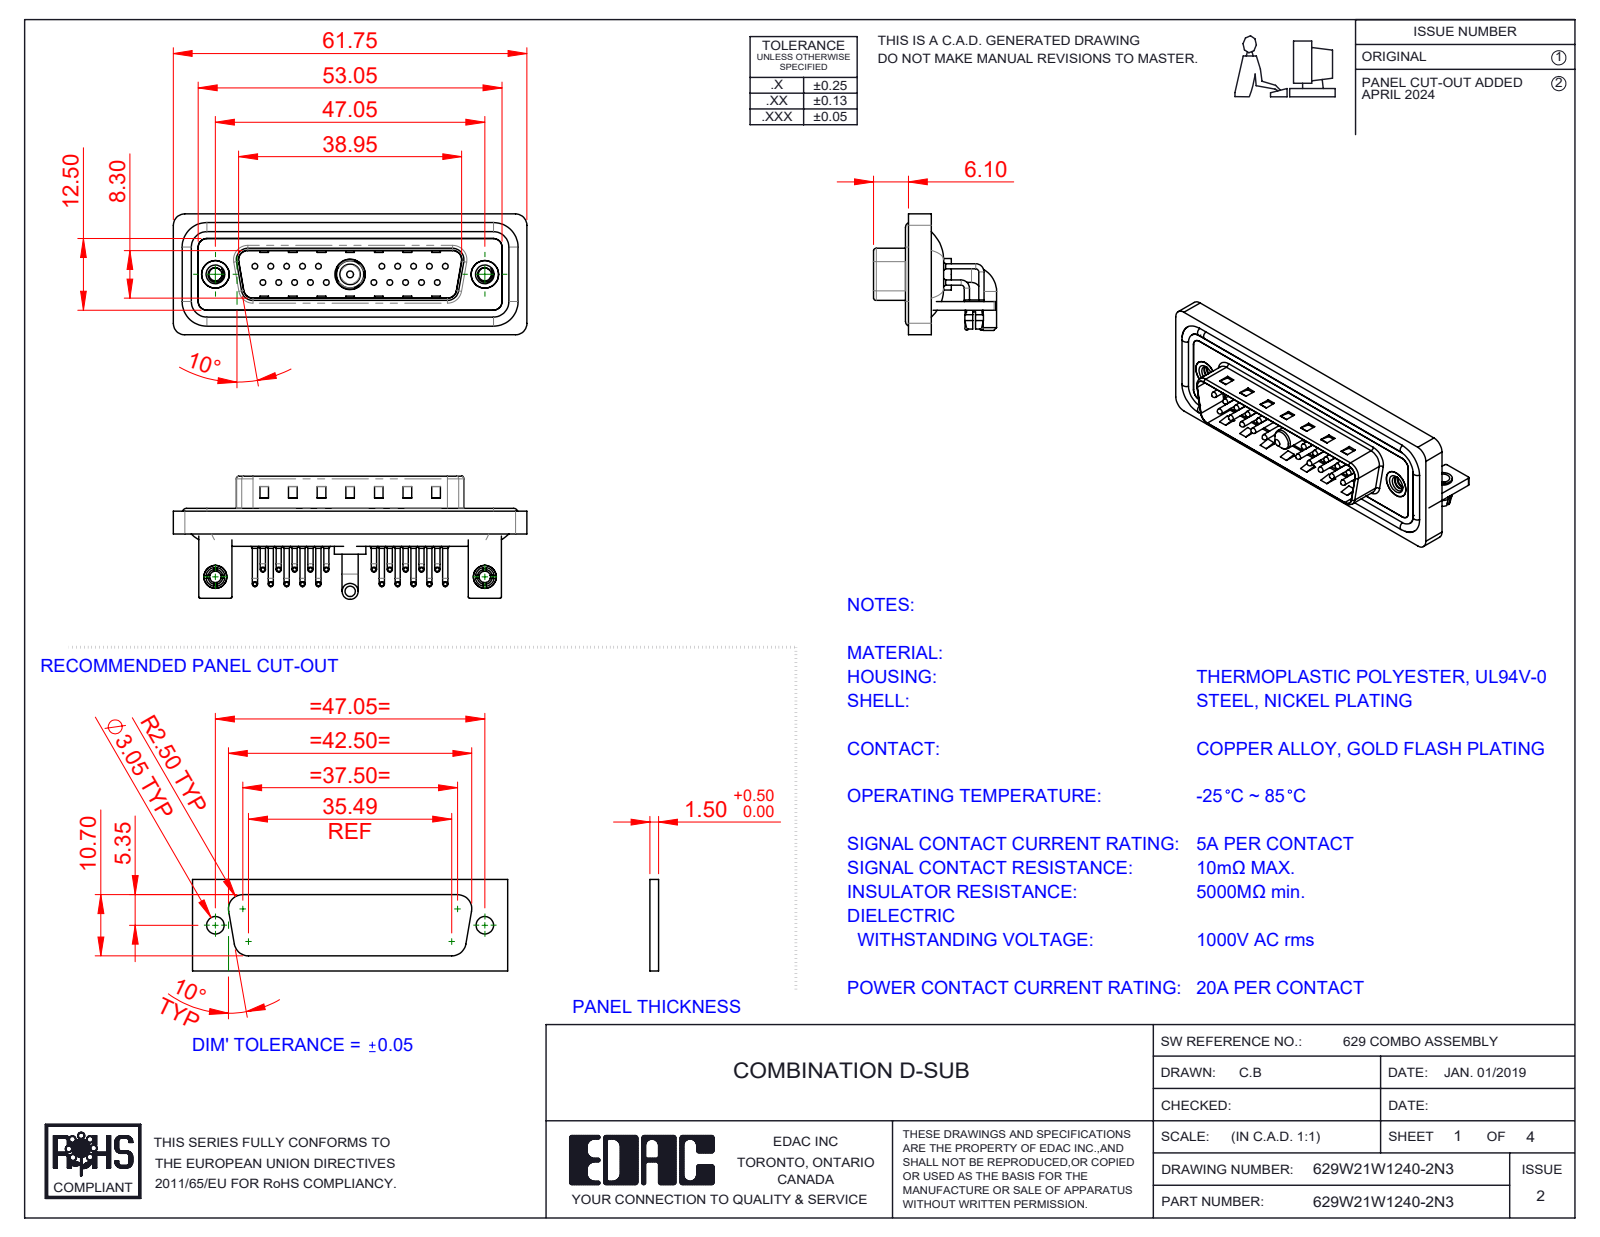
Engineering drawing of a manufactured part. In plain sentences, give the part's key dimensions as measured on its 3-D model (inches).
The part is named "629Combo Shell Rear_25 Contacts; 629Combo Stabilizer Bracket; 629Combo Contact Row 2; 629W21W1140-2N3 (+7 more)". Its 3-D file was written by "SolidWorks 2023 (CONFIG_CONTROL_DESIGN)". It is 33 solids with 2858 faces: 1567 planar, 979 cylindrical and 312 other. Overall it measures 2.431 by 0.846 by 0.831 inches. Its volume is 0.472 cubic inches and its surface area 20.95 square inches. Round holes: 22 of diameter 0.079, 20 of diameter 0.03, 20 of diameter 0.063, 2 of diameter 0.089, 2 of diameter 0.098, 2 of diameter 0.126, 2 of diameter 0.157, 2 of diameter 0.189, 2 of diameter 0.197, 1 of diameter 0.191, 1 of diameter 0.209. Round bosses or shafts: 40 of diameter 0.035, 20 of diameter 0.059, 20 of diameter 0.039, 20 of diameter 0.026, 4 of diameter 0.063, 2 of diameter 0.193, 2 of diameter 0.157, 2 of diameter 0.134. Partial cylindrical surfaces (rounded edges, fillets, slot ends): 20 of radius 0.04, 19 of radius 0.079, 18 of radius 0.059, 16 of radius 0.01, 9 of radius 0.02, 8 of radius 0.063, 4 of radius 0.024, 4 of radius 0.026. The main face-to-face distances are 0.016, 0.031, 0.083, 0.114, 0.059, 0.043, 0.161, 0.063, 0.177, 0.146. The hole center spacings are 0.124, 0.109, 0.218, 0.327, 0.198, 0.763, 0.826, 0.872.
